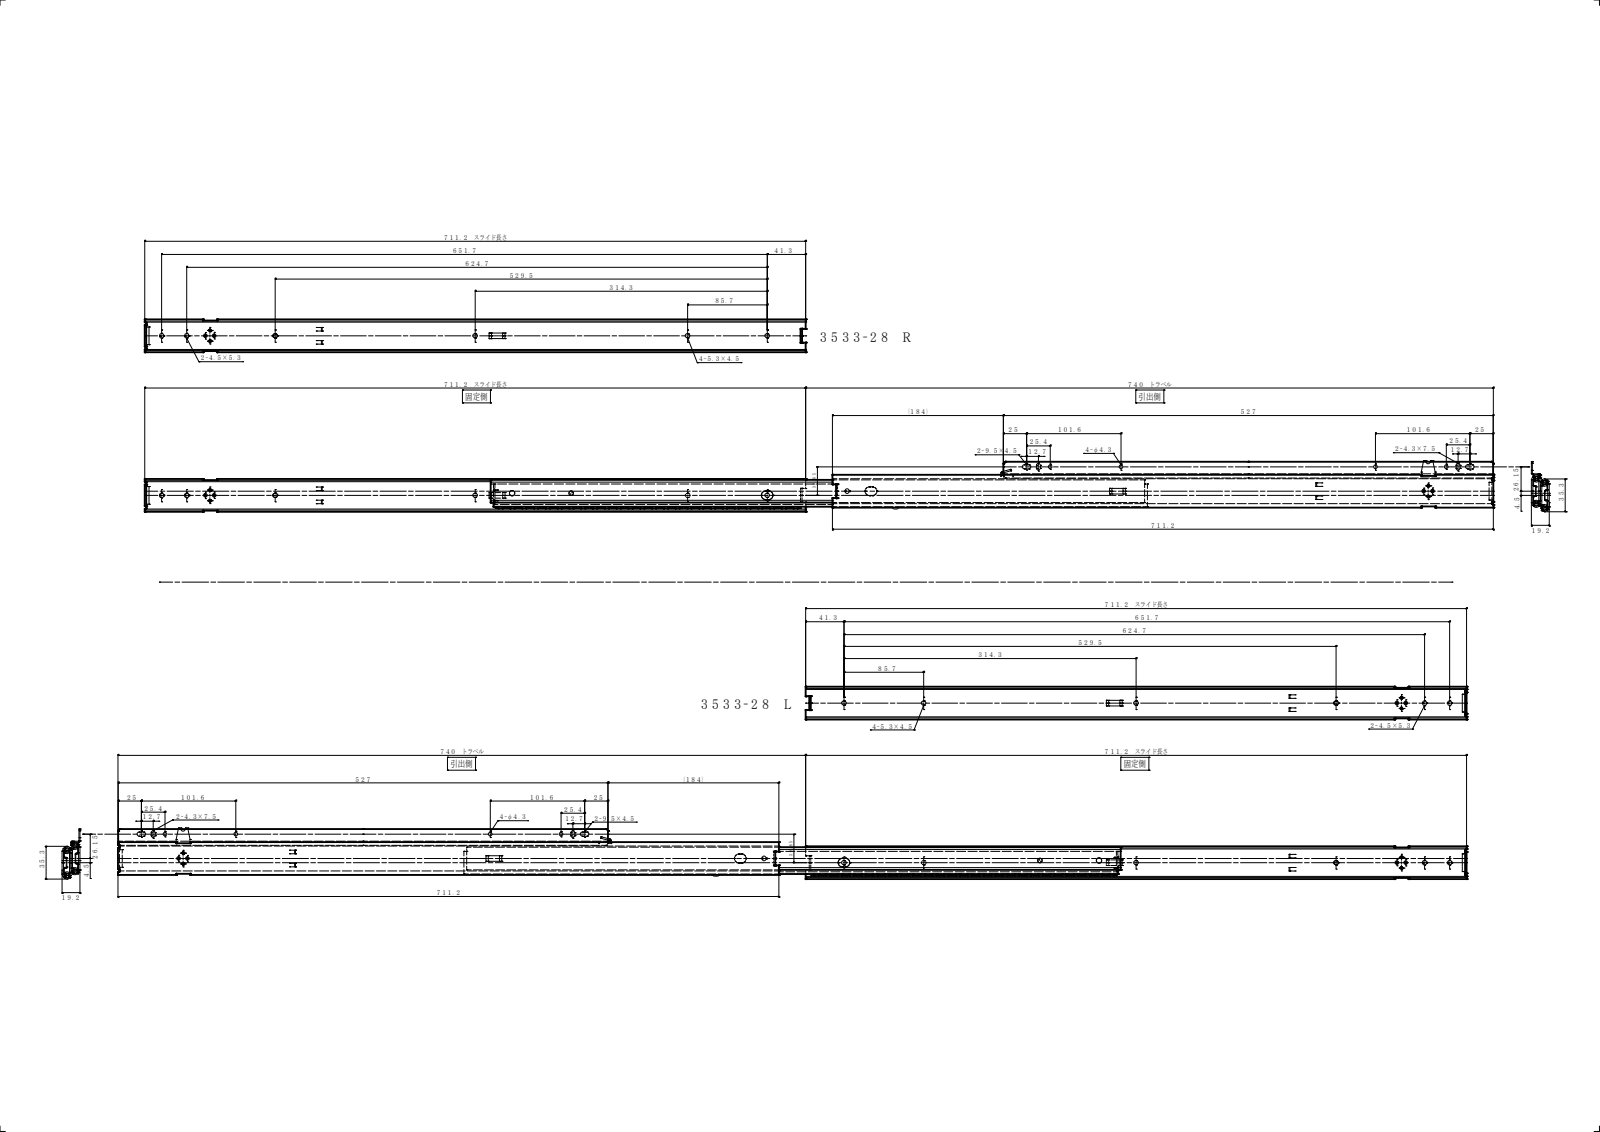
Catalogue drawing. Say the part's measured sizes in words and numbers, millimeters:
The part is named "3533-28R IMドロ側; PN41-3; PN101; PN26 (+8 more)". Its 3-D file was written by "SolidWorks 2019 (CONFIG_CONTROL_DESIGN)". It is 20 solids with 1205 faces: 642 planar, 510 cylindrical and 53 other. Overall it measures 1451.2 by 450 by 54.85 millimeters. Its volume is 384 437 cubic millimeters and its surface area 527 965 square millimeters. Round holes: 4 of diameter 2.3, 4 of diameter 2.7, 4 of diameter 4.2, 4 of diameter 4.3, 3 of diameter 5, 2 of diameter 1.6, 2 of diameter 2.4, 2 of diameter 2.8, 2 of diameter 4.5, 2 of diameter 5.1, 2 of diameter 6. Partial cylindrical surfaces (rounded edges, fillets, slot ends): 32 of radius 2, 28 of radius 0.5, 24 of radius 0.4, 24 of radius 1, 18 of radius 2.25, 13 of radius 1.6, 8 of radius 0.2, 8 of radius 1.3. The main face-to-face distances are 1.6, 9.6, 430.8, 8, 421.2, 17.6, 422.8, 438.8, 429.2, 440.4. The hole center spacings are 7.46, 16.06, 1311.01, 9.5, 10.25, 11.5, 19.75, 63.6.
